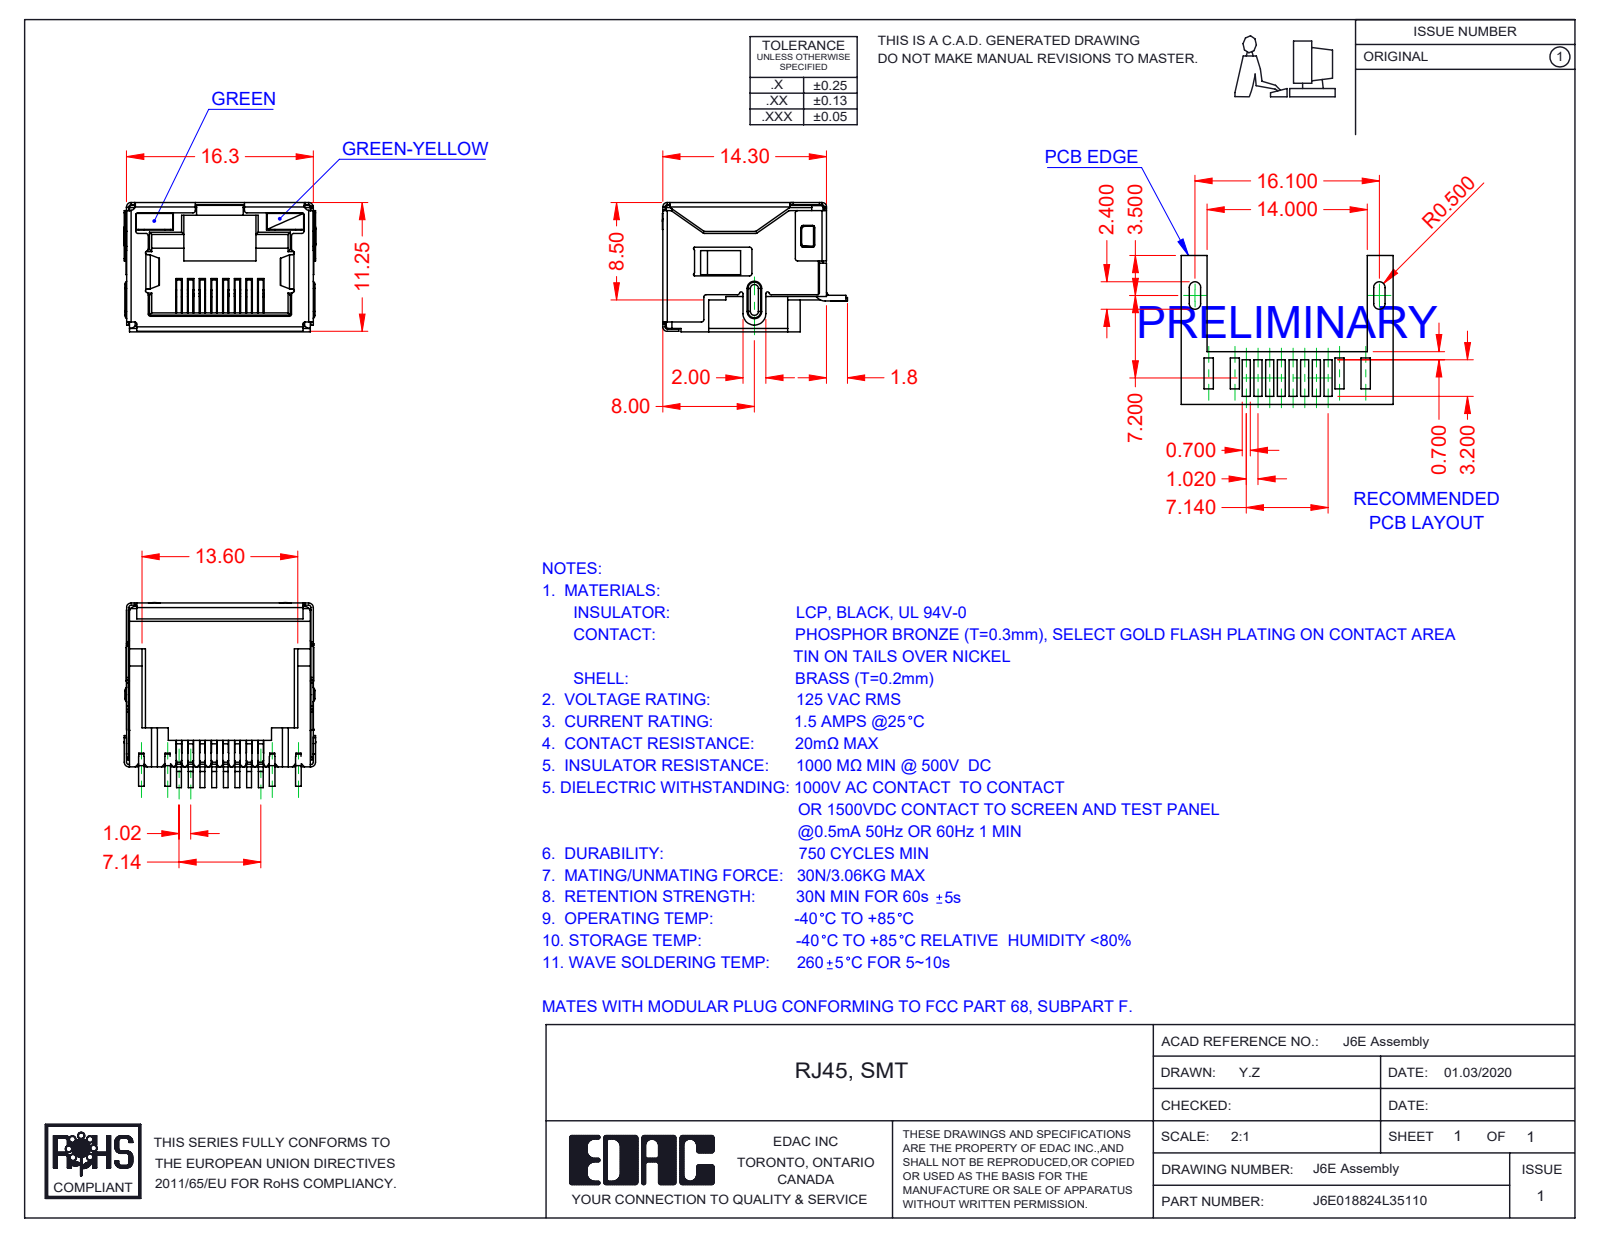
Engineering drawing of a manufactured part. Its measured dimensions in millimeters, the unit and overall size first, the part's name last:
Units: millimetres
Overall size (bounding box): 16.75 × 16.15 × 11.3
Partial cylindrical surfaces — rounded edges, fillets, slot ends (radius × count): R0.2 ×82, R0.25 ×17, R0.4 ×13, R0.5 ×13, R0.1 ×10, R0.15 ×7, R0.3 ×4, R1 ×3
Main face-to-face distances: 11.05, 16.05, 16.1, 15.85, 11.1, 11.3, 2.4, 0.7, 9.85, 0.49
Volume: 1 109 mm³ · Surface area: 4 045 mm²
Bodies: 12 solids, 1498 faces (1099 planar, 349 cylindrical, 50 other)
Part name (STEP PRODUCT): 6E Insulator_LED; 6E Shield_LED; 6E LED RH_5-Green-Yellow; 6E LED LH_3-Green (+2 more)
STEP written by: SolidWorks 2016 (CONFIG_CONTROL_DESIGN)
